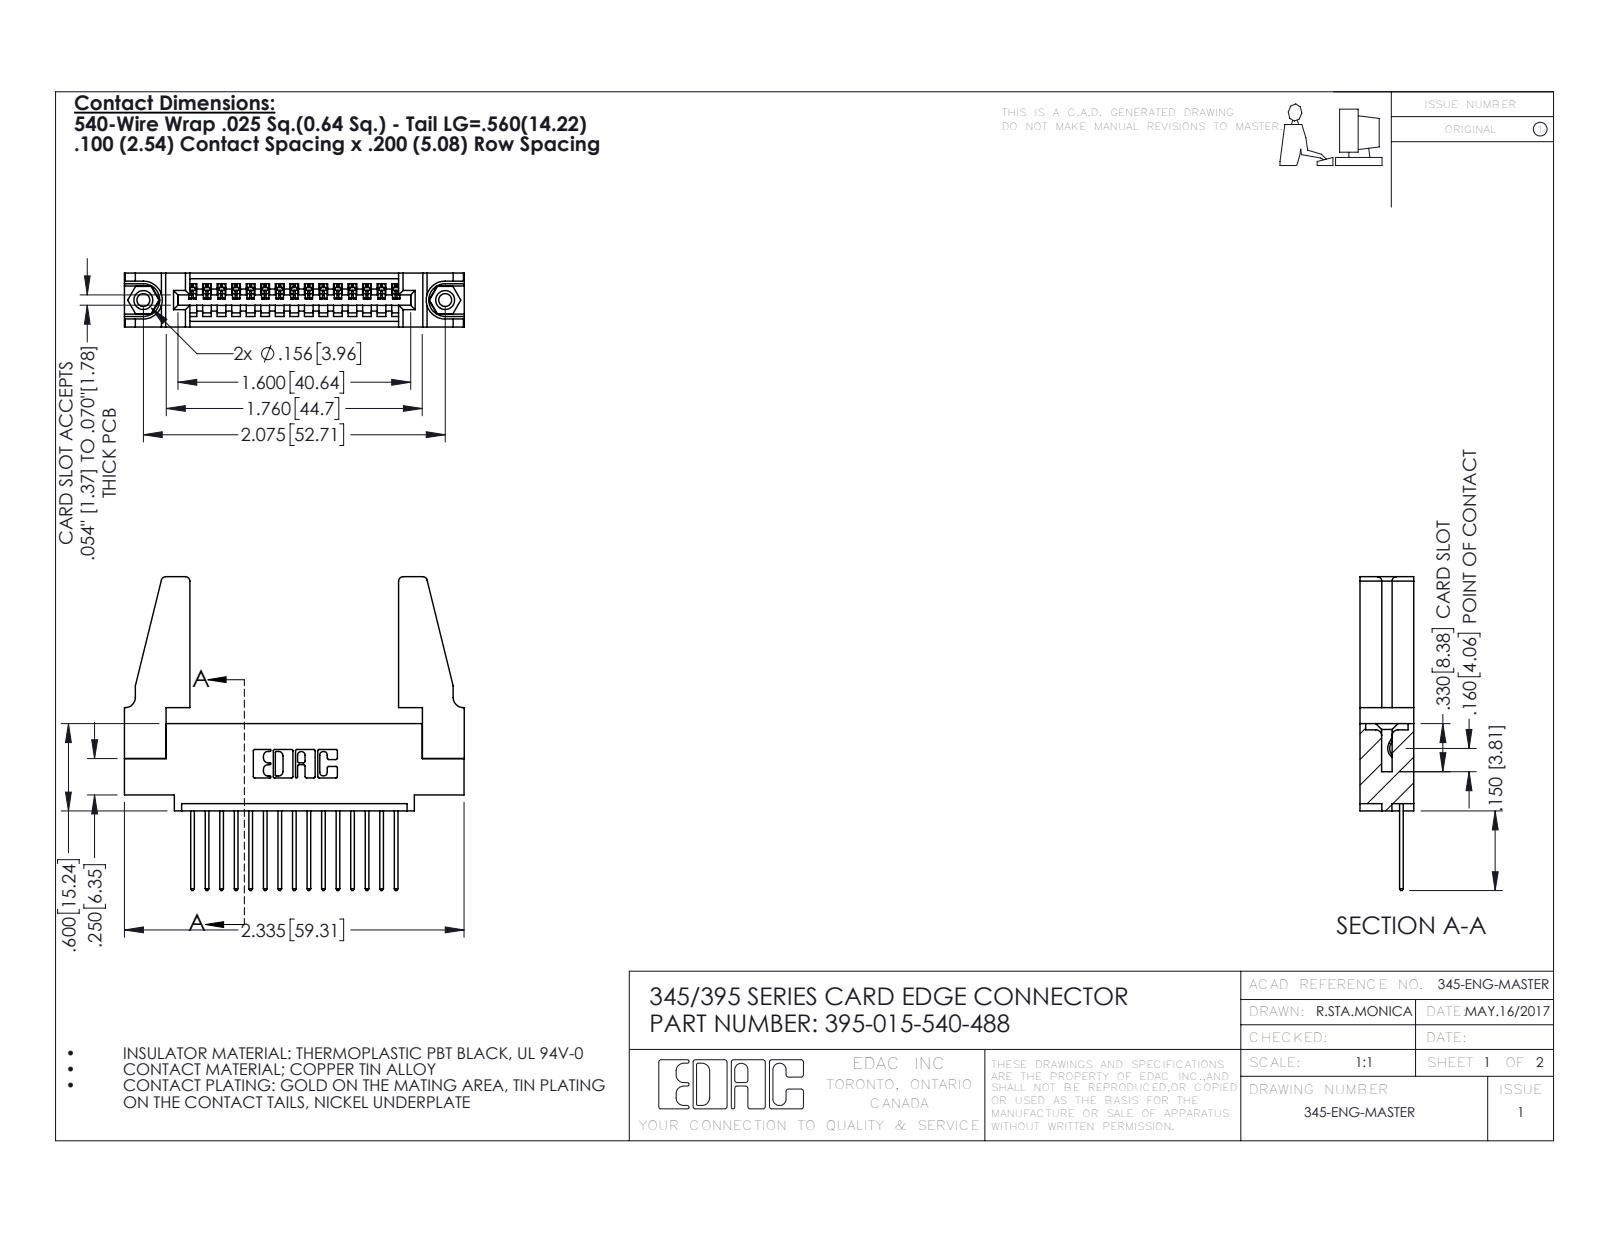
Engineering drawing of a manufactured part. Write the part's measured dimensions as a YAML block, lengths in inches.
part_name: "345-292-001_345-293-140; 345-220-078_345-220-088; 395-015-540-488; 345-250-001_345-250-001-102 (+1 more)"
step_written_by: "SolidWorks 2016 (CONFIG_CONTROL_DESIGN)"
units: inches
bodies: {solids: 20, faces: 1124, planar: 756, cylindrical: 352, other: 16}
overall_size: [2.336, 2.157, 0.37]
volume: 0.526
surface_area: 15.68
round_holes:
  - {diameter: 0.089, count: 2}
  - {diameter: 0.125, count: 2}
  - {diameter: 0.156, count: 2}
  - {diameter: 0.064, count: 1}
round_bosses_or_shafts:
  - {diameter: 0.155, count: 2}
partial_cylinders:
  - {radius: 0.006, count: 30}
  - {radius: 0.01, count: 30}
  - {radius: 0.01, count: 22}
  - {radius: 0.03, count: 8}
  - {radius: 0.007, count: 6}
  - {radius: 0.031, count: 6}
  - {radius: 0.026, count: 3}
  - {radius: 0.031, count: 2}
face_to_face_distances: [0.37, 0.072, 0.298, 0.2, 0.098, 0.272, 0.025, 0.225, 0.148, 0.15]
hole_center_spacings: [0.27, 1.842, 2.075]
